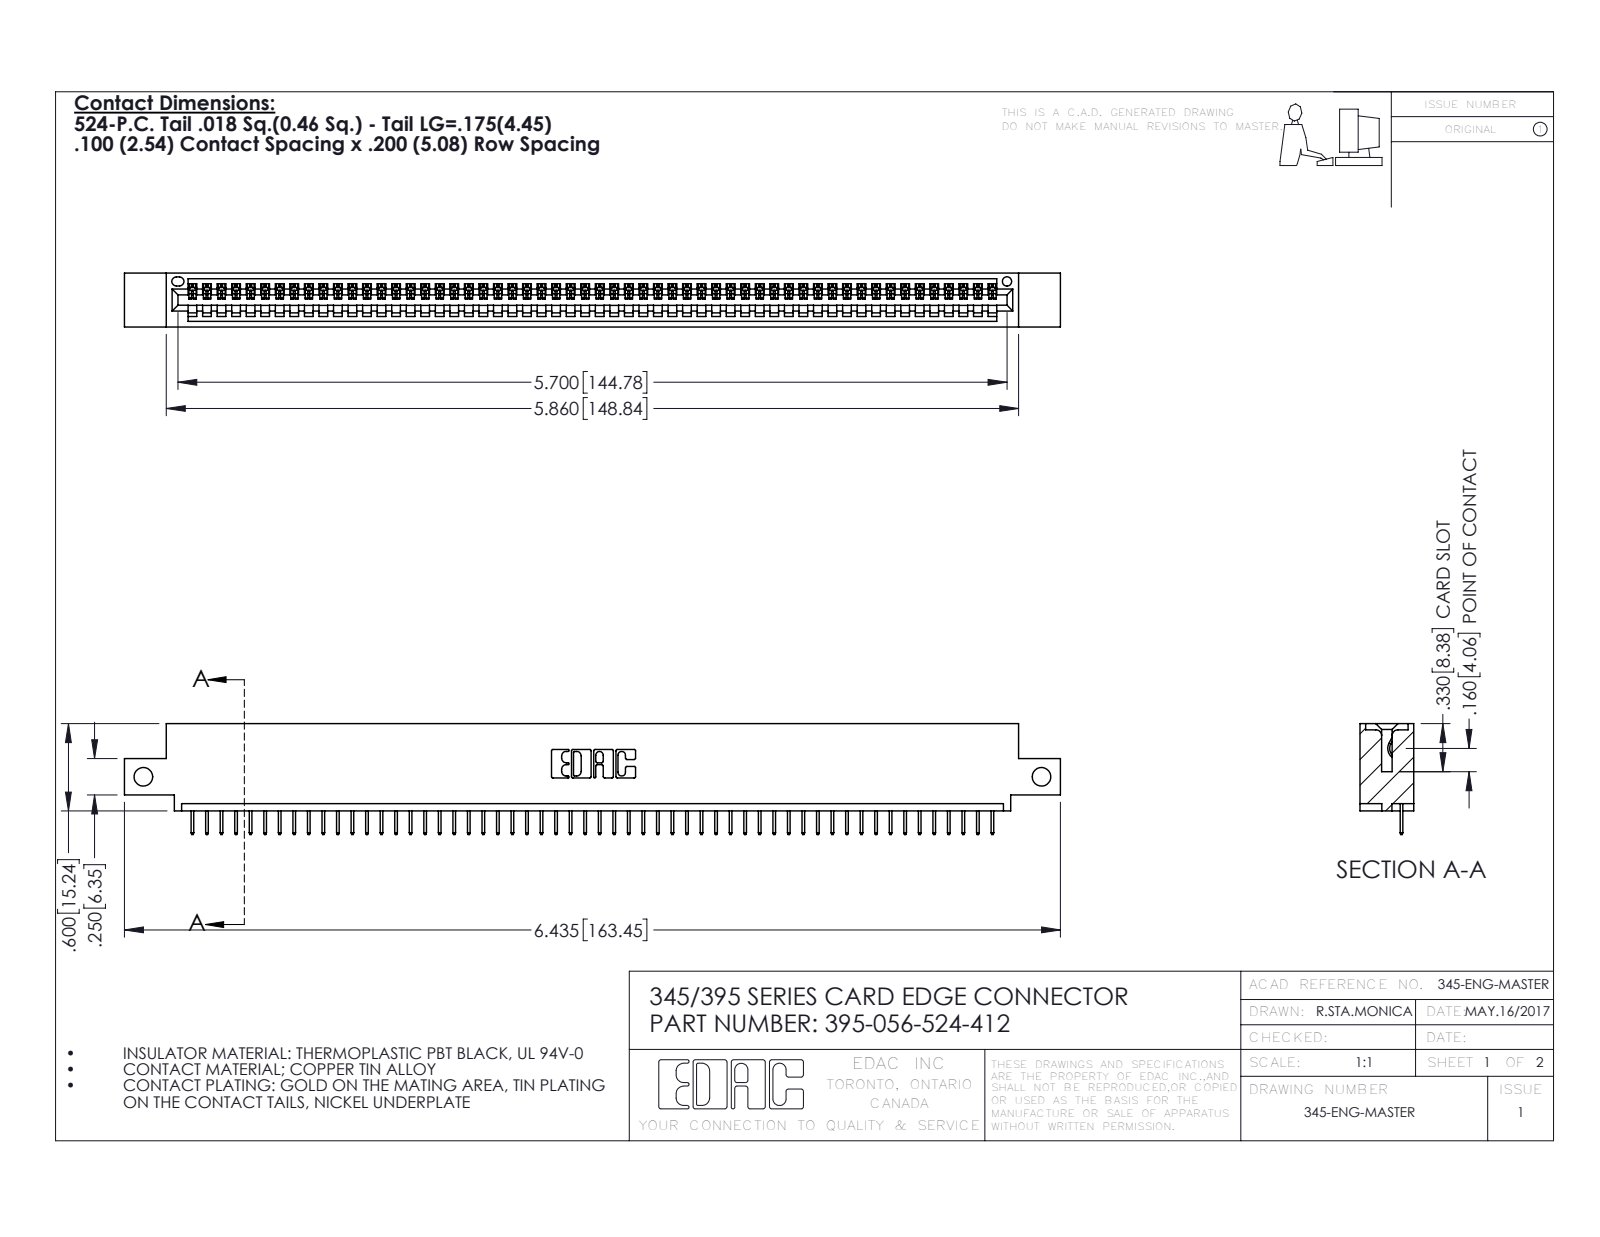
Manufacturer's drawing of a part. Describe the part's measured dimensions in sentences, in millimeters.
The part is named "345-292-001_345-293-124; 345 Part_0.110 Offset - Side Mount; 395-056-524-412". Its 3-D file was written by "SolidWorks 2016 (CONFIG_CONTROL_DESIGN)". It is 57 solids with 3602 faces: 2660 planar, 942 cylindrical and 0 other. Overall it measures 163.4 by 19.4 by 9.4 millimeters. Its volume is 15 300 cubic millimeters and its surface area 19 700 square millimeters. Round holes: 2 of diameter 3.3, 1 of diameter 1.6. Partial cylindrical surfaces (rounded edges, fillets, slot ends): 112 of radius 0.2, 22 of radius 0.3, 6 of radius 0.2, 6 of radius 0.8, 3 of radius 0.7, 2 of radius 0.8, 2 of radius 1, 1 of radius 0.4. The main face-to-face distances are 1.8, 7.6, 9.4, 5.1, 2.5, 6.9, 0.6, 5.7, 1.8, 3.8. The hole center spacings are 156.8.
